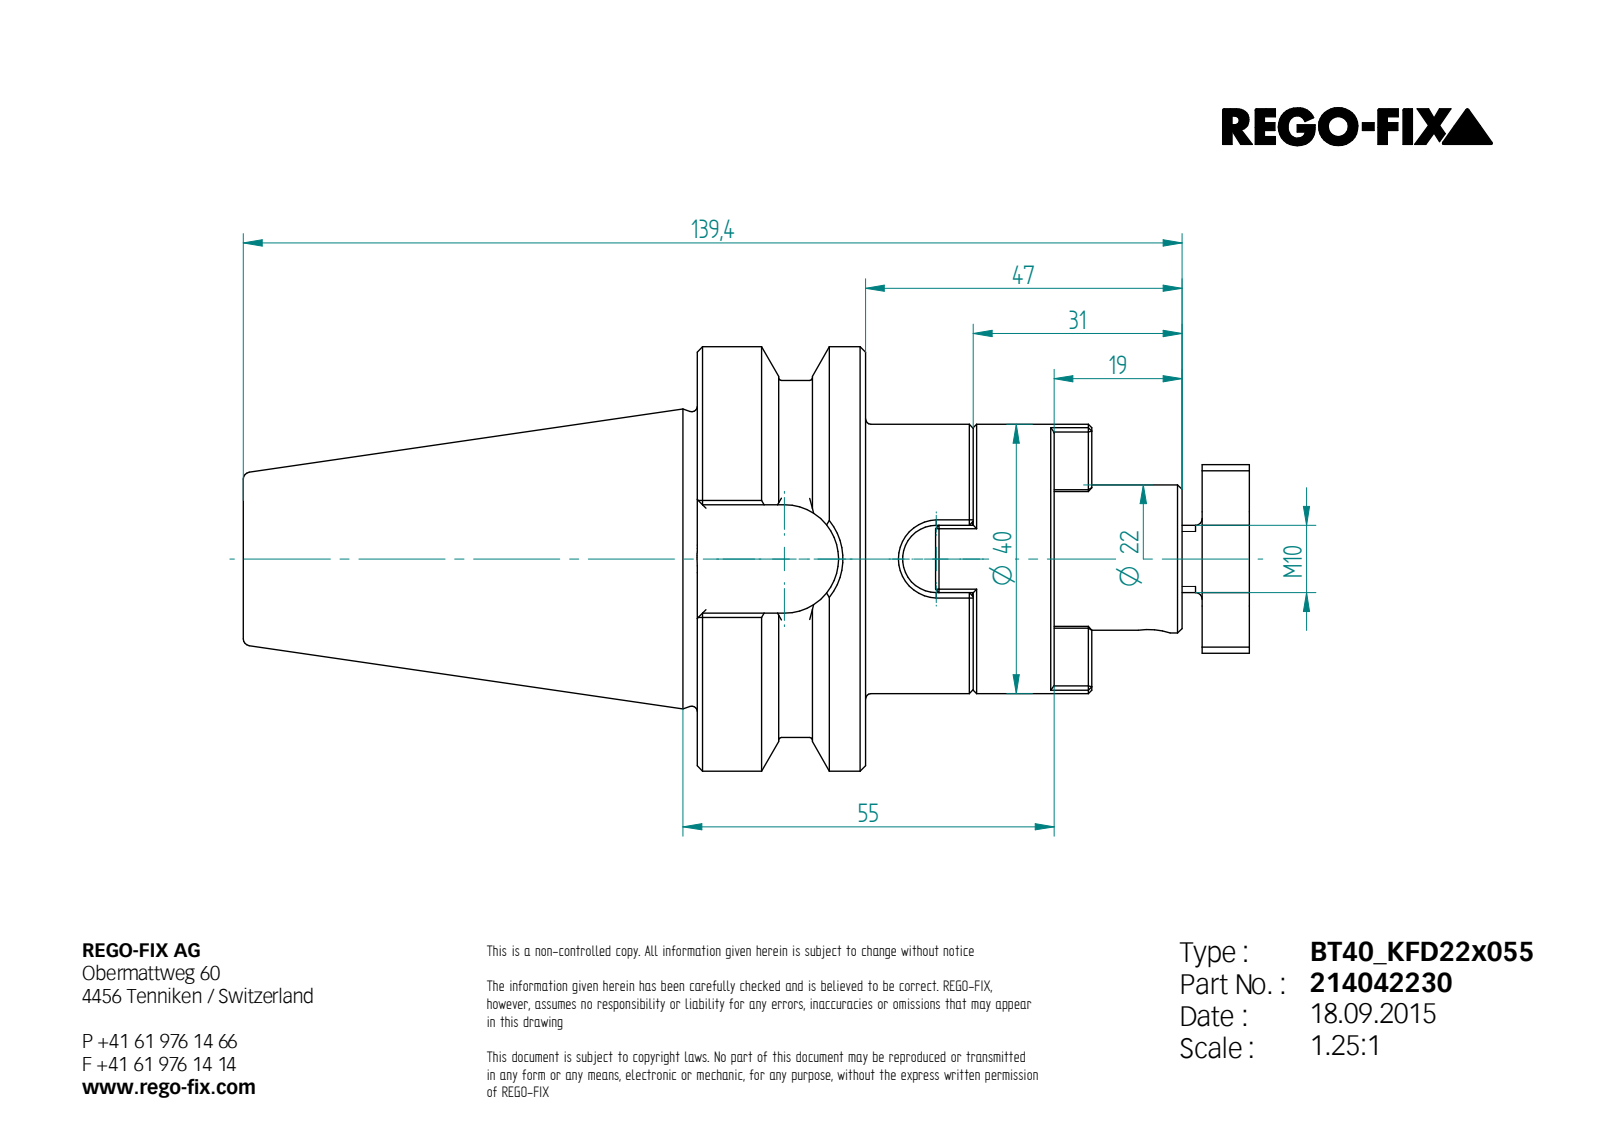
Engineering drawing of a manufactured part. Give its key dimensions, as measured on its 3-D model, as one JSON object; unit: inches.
{"step_written_by": "Unknown (AUTOMOTIVE_DESIGN)", "units": "inches", "bodies": {"solids": 3, "faces": 215, "planar": 126, "cylindrical": 35, "other": 54}, "overall_size": [5.882, 2.48, 2.48], "volume_in3": 9.977, "surface_area_in2": 54.53, "round_holes": [[0.33, 1], [0.413, 1], [0.545, 1], [0.669, 1], [0.866, 1]], "round_bosses_or_shafts": [[2.48, 1], [2.087, 1], [1.575, 1], [0.843, 1], [0.394, 1]], "partial_cylinders_radius": [[0.02, 4], [0.079, 4], [0.118, 2], [0.197, 1], [0.317, 1], [0.551, 1]], "face_to_face_distances": [1.614, 0.63, 0.984, 2.087, 1.102, 0.472, 0.394, 2.244, 3.228, 1.142]}
